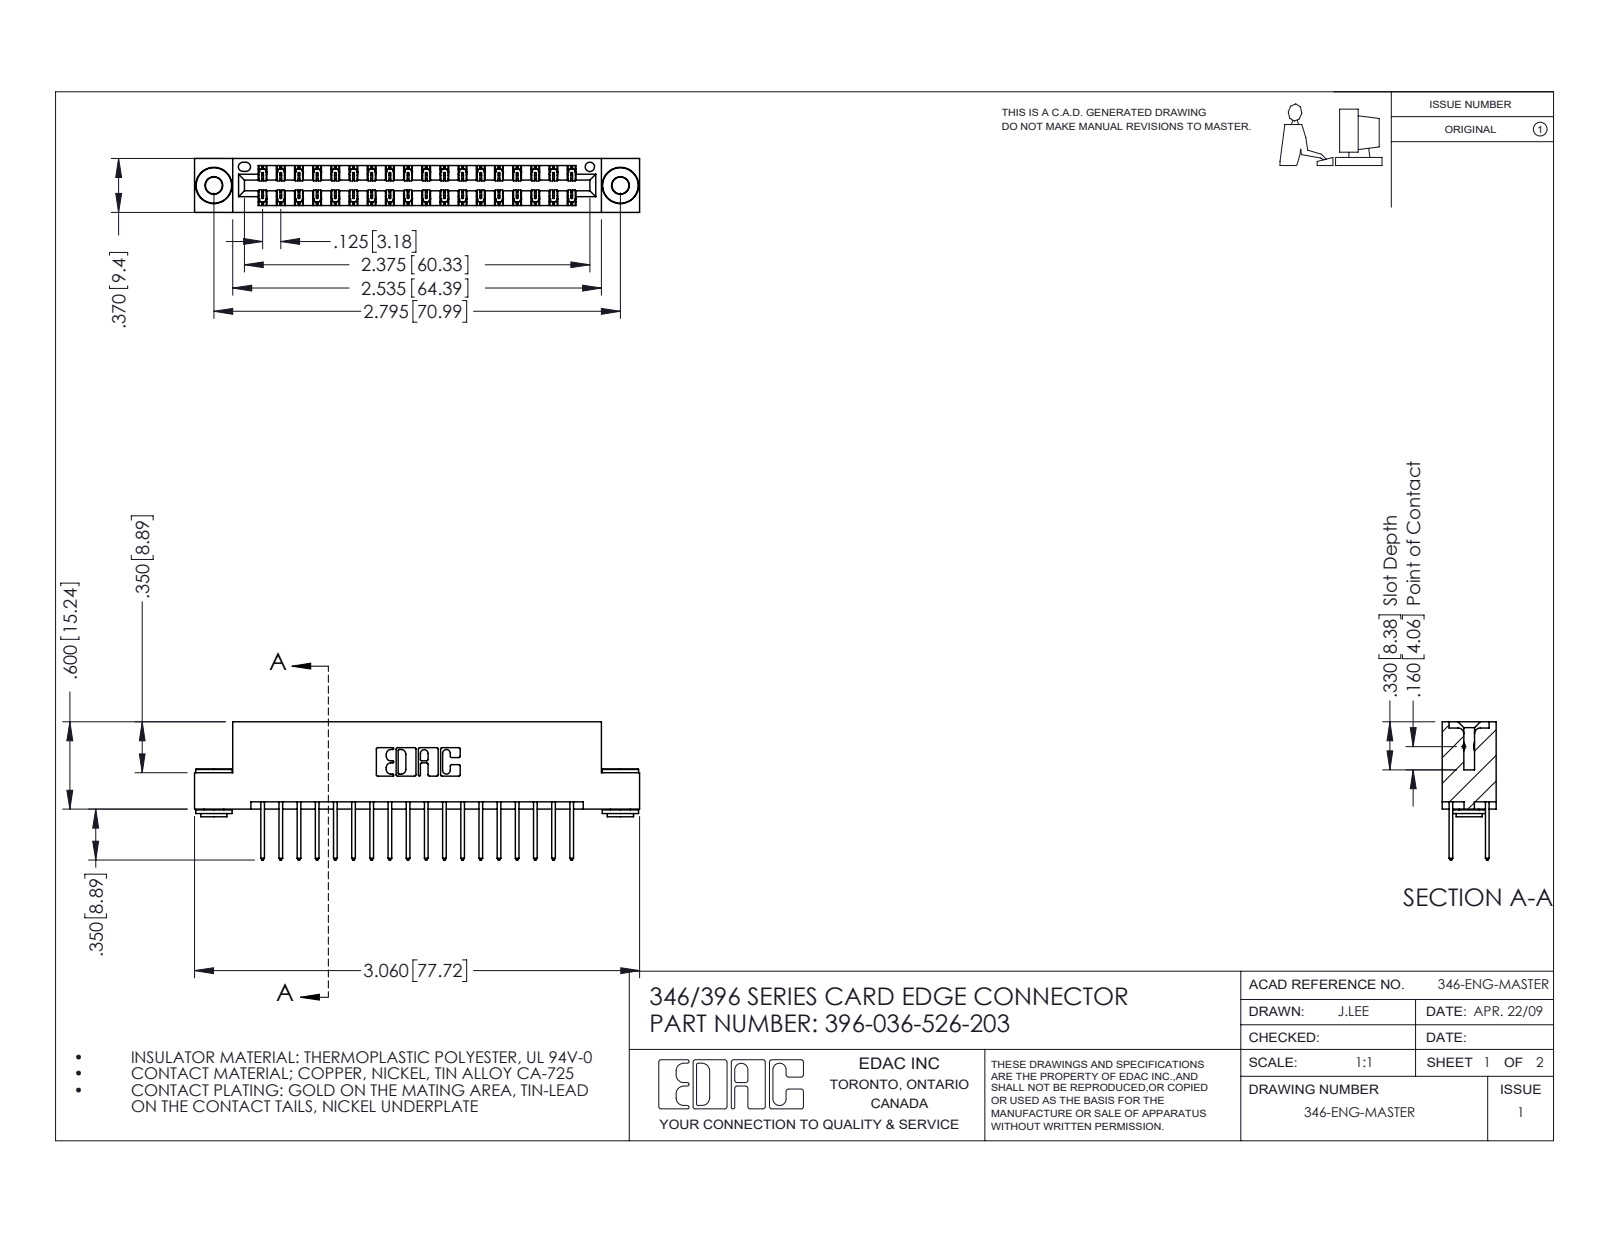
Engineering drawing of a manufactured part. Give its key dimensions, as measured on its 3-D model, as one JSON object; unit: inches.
{"part_name": "345-292-001_345-293-126; 346 Part_Flush Mounting Lugs - 0.156 Dia-TH; 396-036-526-203; 345-250-002_345-250-002-102", "step_written_by": "SolidWorks 2016 (CONFIG_CONTROL_DESIGN)", "units": "inches", "bodies": {"solids": 39, "faces": 2032, "planar": 1346, "cylindrical": 678, "other": 8}, "overall_size": [3.06, 0.95, 0.37], "volume_in3": 0.456, "surface_area_in2": 16.07, "round_holes": [[0.116, 2], [0.156, 2], [0.064, 1]], "round_bosses_or_shafts": [[0.25, 2], [0.18, 2], [0.136, 2]], "partial_cylinders_radius": [[0.006, 54], [0.01, 36], [0.01, 22], [0.007, 6], [0.031, 6], [0.026, 3], [0.014, 2], [0.022, 2]], "face_to_face_distances": [0.048, 0.322, 0.25, 0.37, 0.025, 0.072, 0.298, 0.275, 0.148, 0.222], "hole_center_spacings": [0.246, 2.588, 2.795]}
